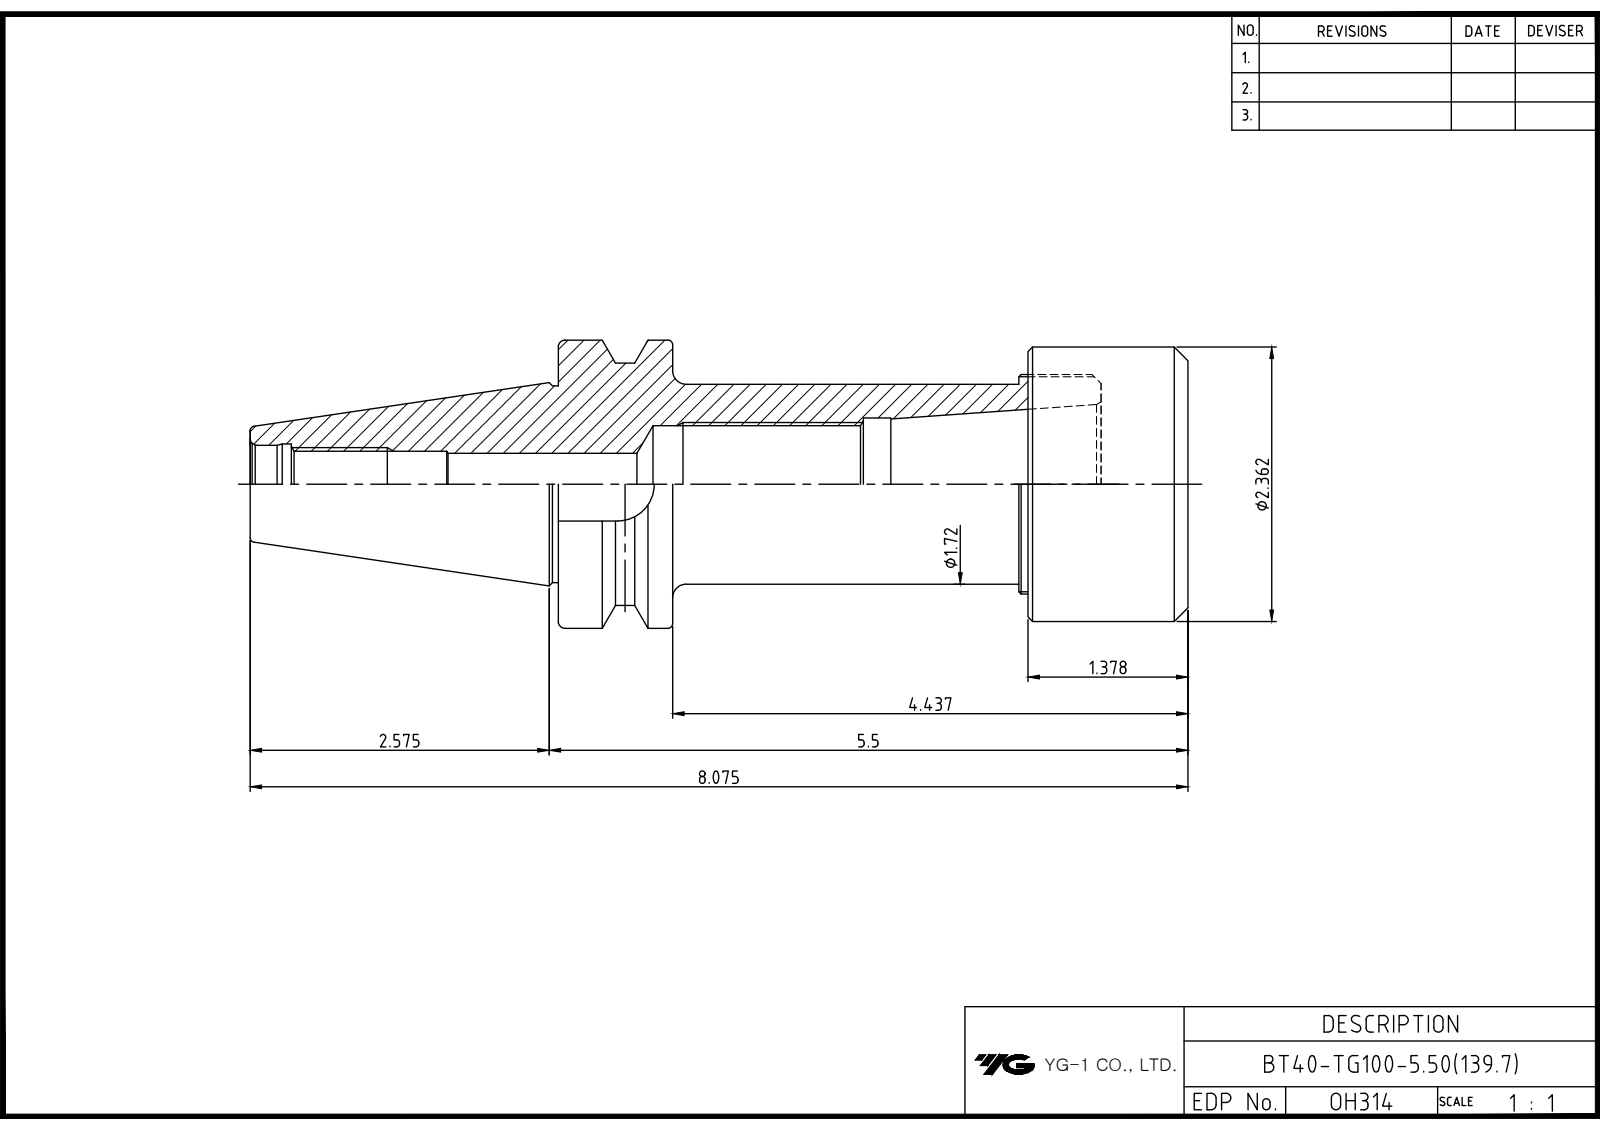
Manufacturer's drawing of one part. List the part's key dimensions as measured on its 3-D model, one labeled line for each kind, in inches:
Part name (STEP PRODUCT): BT40-TG100-139.7; LO-BT40-TG100-139.7; TG100 NUT
STEP written by: Autodesk Inventor 2022 (AUTOMOTIVE_DESIGN)
Units: inches
Bodies: 2 solids, 62 faces (21 planar, 19 cylindrical, 22 other)
Overall size (bounding box): 8.075 × 2.48 × 2.48
Volume: 15.43 in³ · Surface area: 90.4 in²
Round holes (diameter × count): ⌀0.531 ×1, ⌀0.545 ×1, ⌀0.669 ×1, ⌀0.693 ×1, ⌀0.999 ×1, ⌀1.142 ×1, ⌀1.378 ×1, ⌀1.89 ×1
Round bosses / shafts (diameter × count): ⌀2.48 ×1, ⌀2.362 ×1, ⌀2.071 ×1, ⌀1.732 ×1, ⌀1.72 ×1
Partial cylindrical surfaces — rounded edges, fillets, slot ends (radius × count): R0.317 ×1
Main face-to-face distances: 0.748, 4.673, 5.421, 0.984, 3.689, 4.437, 4.043, 3.059, 0.63, 1.378
